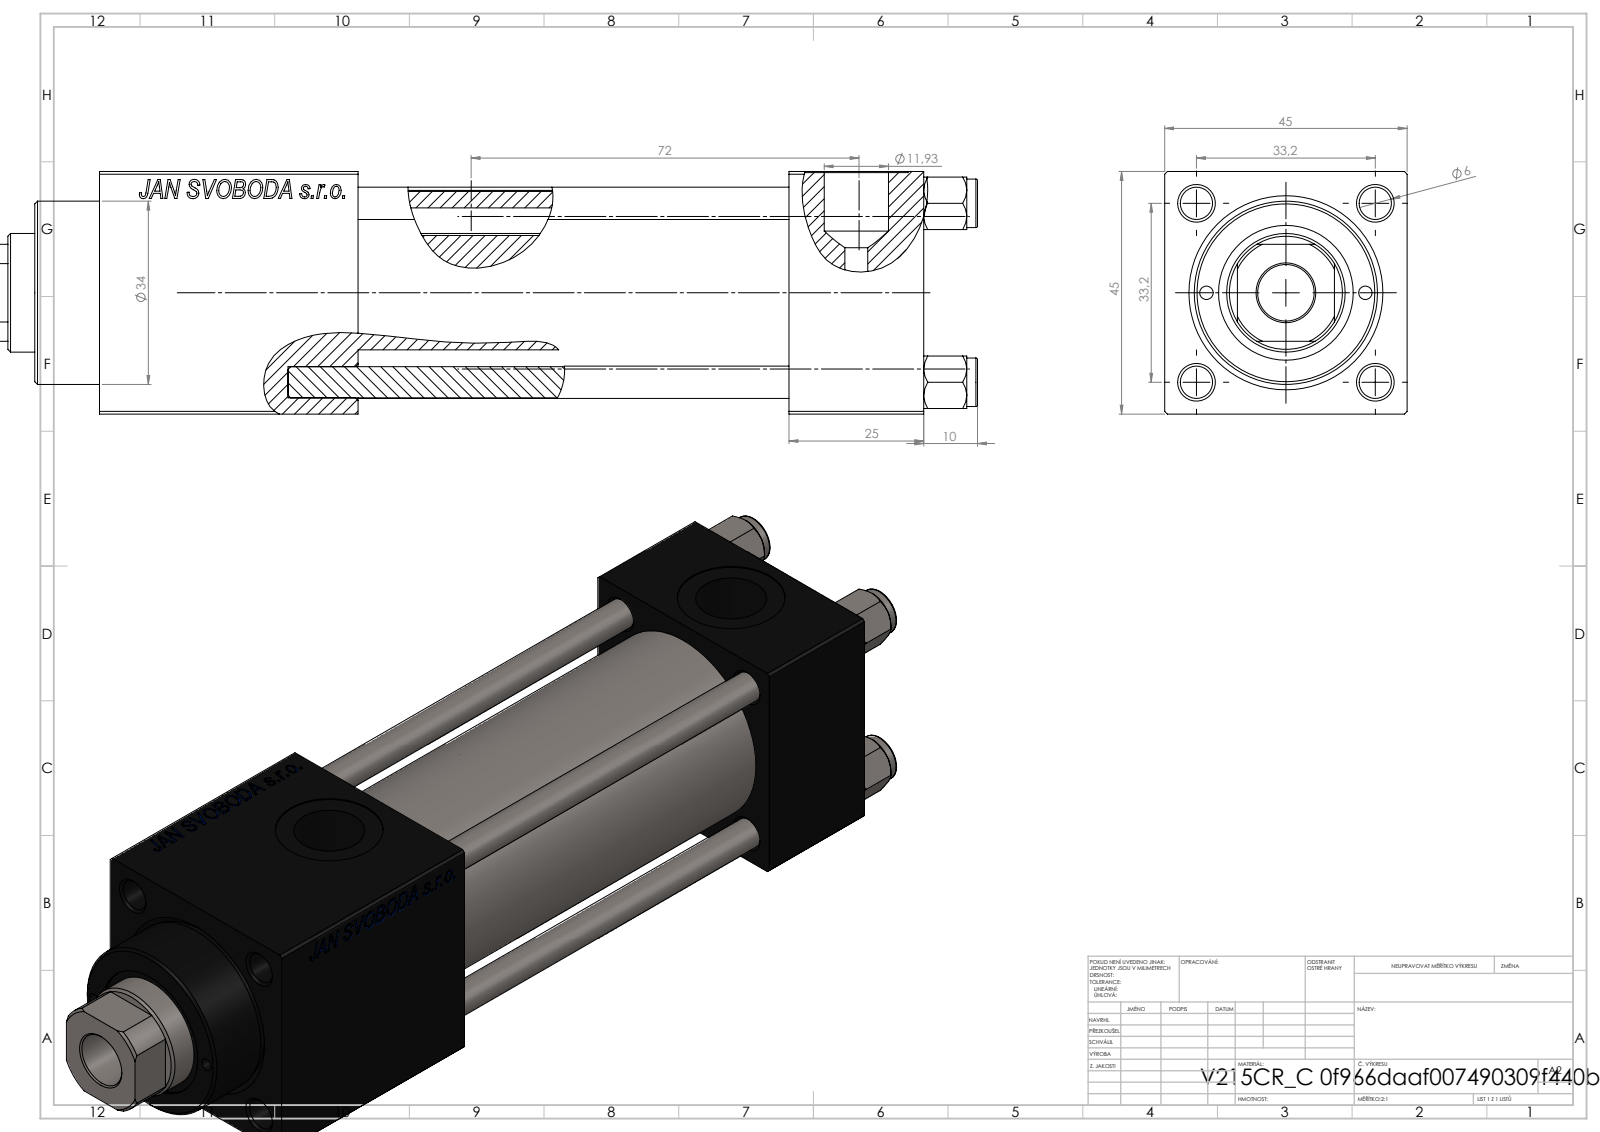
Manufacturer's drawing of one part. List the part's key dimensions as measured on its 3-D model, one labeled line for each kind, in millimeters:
Part name (STEP PRODUCT): V215CR_VCP_C; V215CR_C_TYCINKA; NUT_M5_C; V215_VC_A (+1 more)
STEP written by: SolidWorks 2019 (CONFIG_CONTROL_DESIGN)
Units: millimetres
Bodies: 11 solids, 1154 faces (527 planar, 91 cylindrical, 536 other)
Overall size (bounding box): 188 × 45 × 45
Volume: 234 305 mm³ · Surface area: 82 503 mm²
Round holes (diameter × count): ⌀6 ×4, ⌀2.5 ×2, ⌀7 ×2, ⌀13.16 ×2, ⌀20 ×2, ⌀10.5 ×1, ⌀22 ×1, ⌀24 ×1, ⌀25 ×1, ⌀32 ×1, ⌀33 ×1
Round bosses / shafts (diameter × count): ⌀9 ×4, ⌀38 ×1, ⌀34 ×1
Partial cylindrical surfaces — rounded edges, fillets, slot ends (radius × count): R10.5 ×1
Main face-to-face distances: 45, 25, 153, 105, 80, 128, 48, 124.3, 99.3, 19.3
Hole centre spacings: 16.7, 23.48, 33.2, 35.47, 14.75, 46.95, 29.5, 105.5
